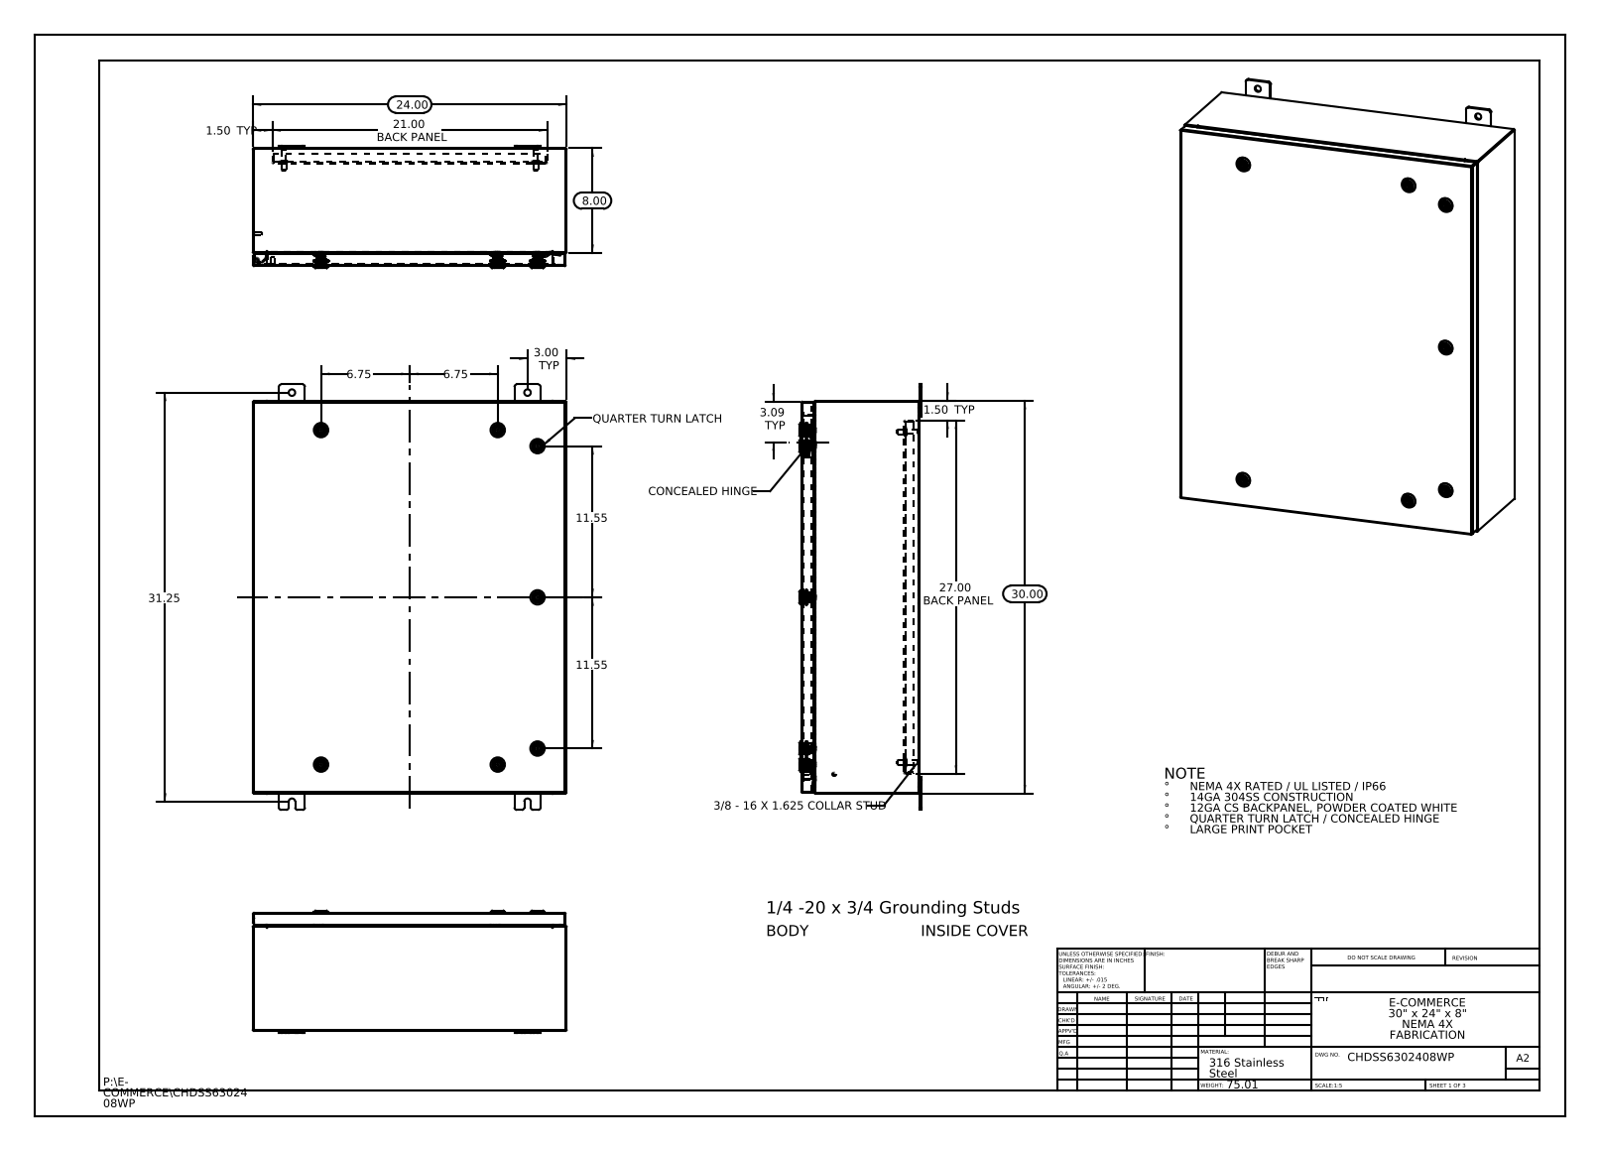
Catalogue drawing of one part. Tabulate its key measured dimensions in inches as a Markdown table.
| quantity | value |
| --- | --- |
| part name | Washer-221320-IB-Industrilas_Washer-221320-IB-Industrilas; Nut-211301-IB-Industrilas_Nut-211301-IB-Industrilas; Housing-211301-IB-Industrilas_Housing-211301-IB-Industrilas; Concealed Hinge enclosure side (+8 more) |
| STEP written by | SolidWorks 2013 (CONFIG_CONTROL_DESIGN) |
| units | inches |
| bodies | 59 solids, 6198 faces (1788 planar, 1928 cylindrical, 2482 other) |
| overall size | 32.5 × 24 × 9.356 |
| volume | 266.7 in³ |
| surface area | 6 614 in² |
| round holes (diameter × count) | 0.5 × 8, 0.197 × 7, 0.394 × 7, 0.4 × 7, 0.63 × 7, 0.787 × 7, 0.136 × 2, 0.211 × 1 |
| round bosses / shafts (diameter × count) | 0.236 × 9, 1.102 × 7, 0.78 × 7, 0.626 × 7, 0.61 × 7, 0.531 × 7, 0.392 × 7, 0.114 × 7 |
| partial cylindrical surfaces (radius × count) | 0.006 × 231, 0.118 × 231, 0.028 × 84, 0.02 × 28, 0.197 × 28, 0.19 × 24, 0.013 × 22, 0.088 × 18 |
| main face-to-face distances | 0.075, 0.074, 9.01, 8.935, 8.936, 8.861, 0.104, 1, 1.075, 7.861 |
| hole center spacings | 1.858, 3.276, 11.55, 13.5, 16.583, 18, 19.25, 25.25 |
